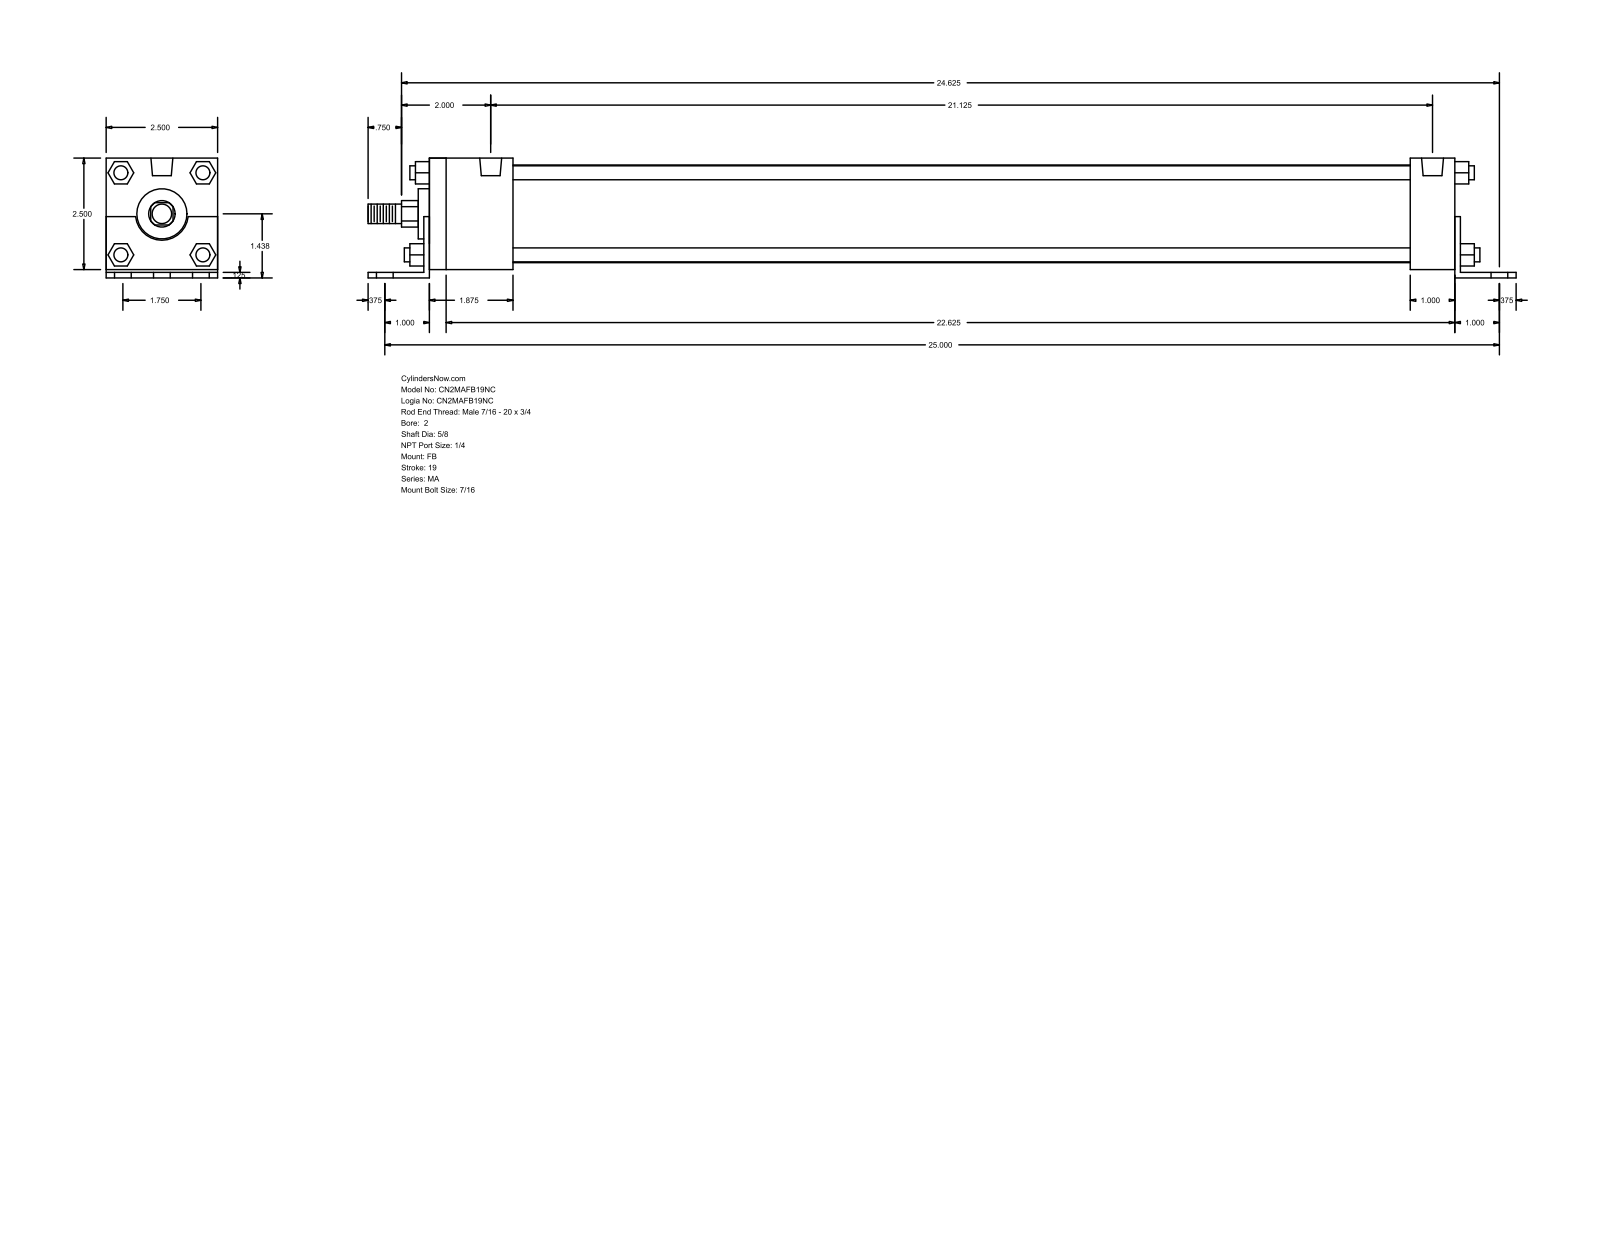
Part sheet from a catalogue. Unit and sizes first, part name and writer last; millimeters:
Units: millimetres
Overall size (bounding box): 654.05 × 68.26 × 63.5
Round holes (diameter × count): ⌀11.11 ×6, ⌀7.94 ×4, ⌀12.49 ×2
Round bosses / shafts (diameter × count): ⌀7.94 ×4, ⌀55.63 ×1, ⌀28.57 ×1, ⌀15.88 ×1, ⌀11.11 ×1
Partial cylindrical surfaces — rounded edges, fillets, slot ends (radius × count): R7.54 ×1, R15.05 ×1
Main face-to-face distances: 63.5, 3.17, 4.76, 68.26, 1.59, 65.09, 590.55, 3.18, 584.2, 587.37
Hole centre spacings: 22.23, 635.4, 635.01, 44.11, 44.46, 64.3, 536.58, 575.11
Bodies: 0 solids, 140 faces (105 planar, 35 cylindrical, 0 other)
Part name (STEP PRODUCT): MA_FB__0200_0.625
STEP written by: GSSL Pune (CONFIG_CONTROL_DESIGN)
